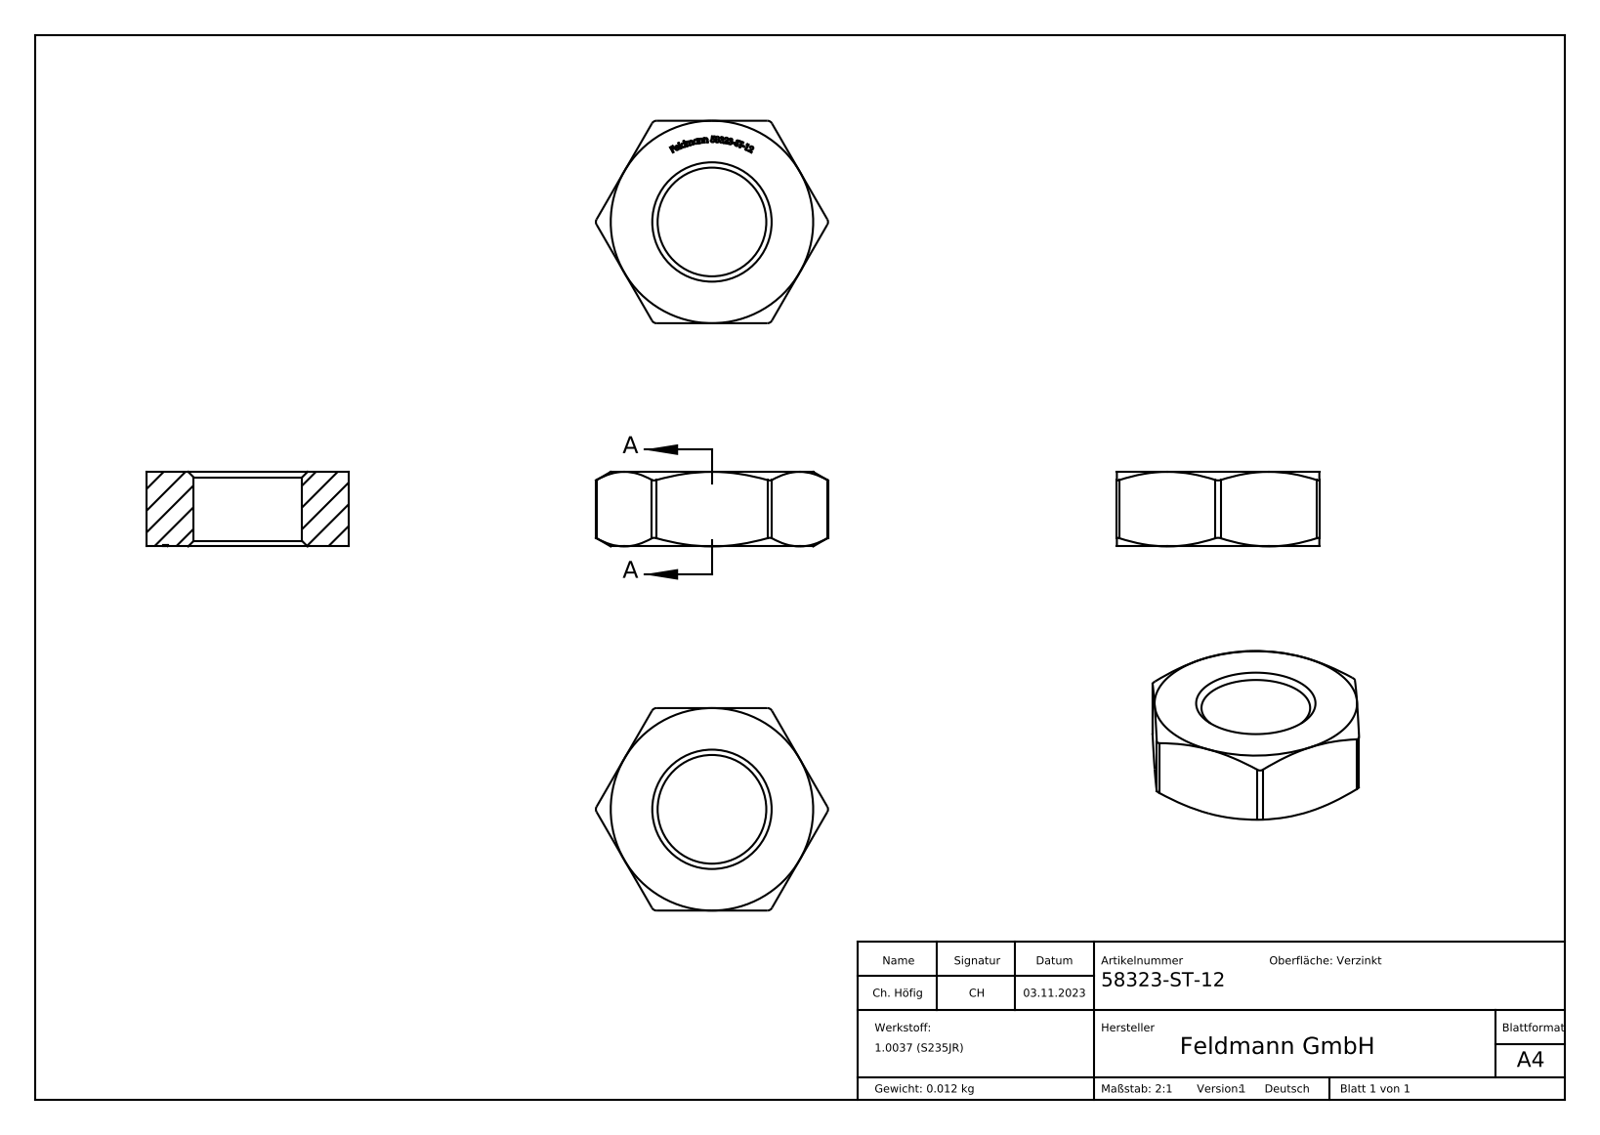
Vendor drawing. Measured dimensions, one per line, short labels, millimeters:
name: 58323-ST-12
written by: SolidWorks 2018 (CONFIG_CONTROL_DESIGN)
unit: mm
bodies: 1 solid, 283 faces (134 planar, 7 cylindrical, 142 other)
size: 21.79 × 19 × 7
volume: 1 593 mm³; area: 1 102 mm²
holes: 1× ⌀10.2
rounds: 6× R0.5
face distances: 19, 7, 6.9, 0.53, 0.54, 0.59, 0.48, 0.34, 0.39, 0.32
